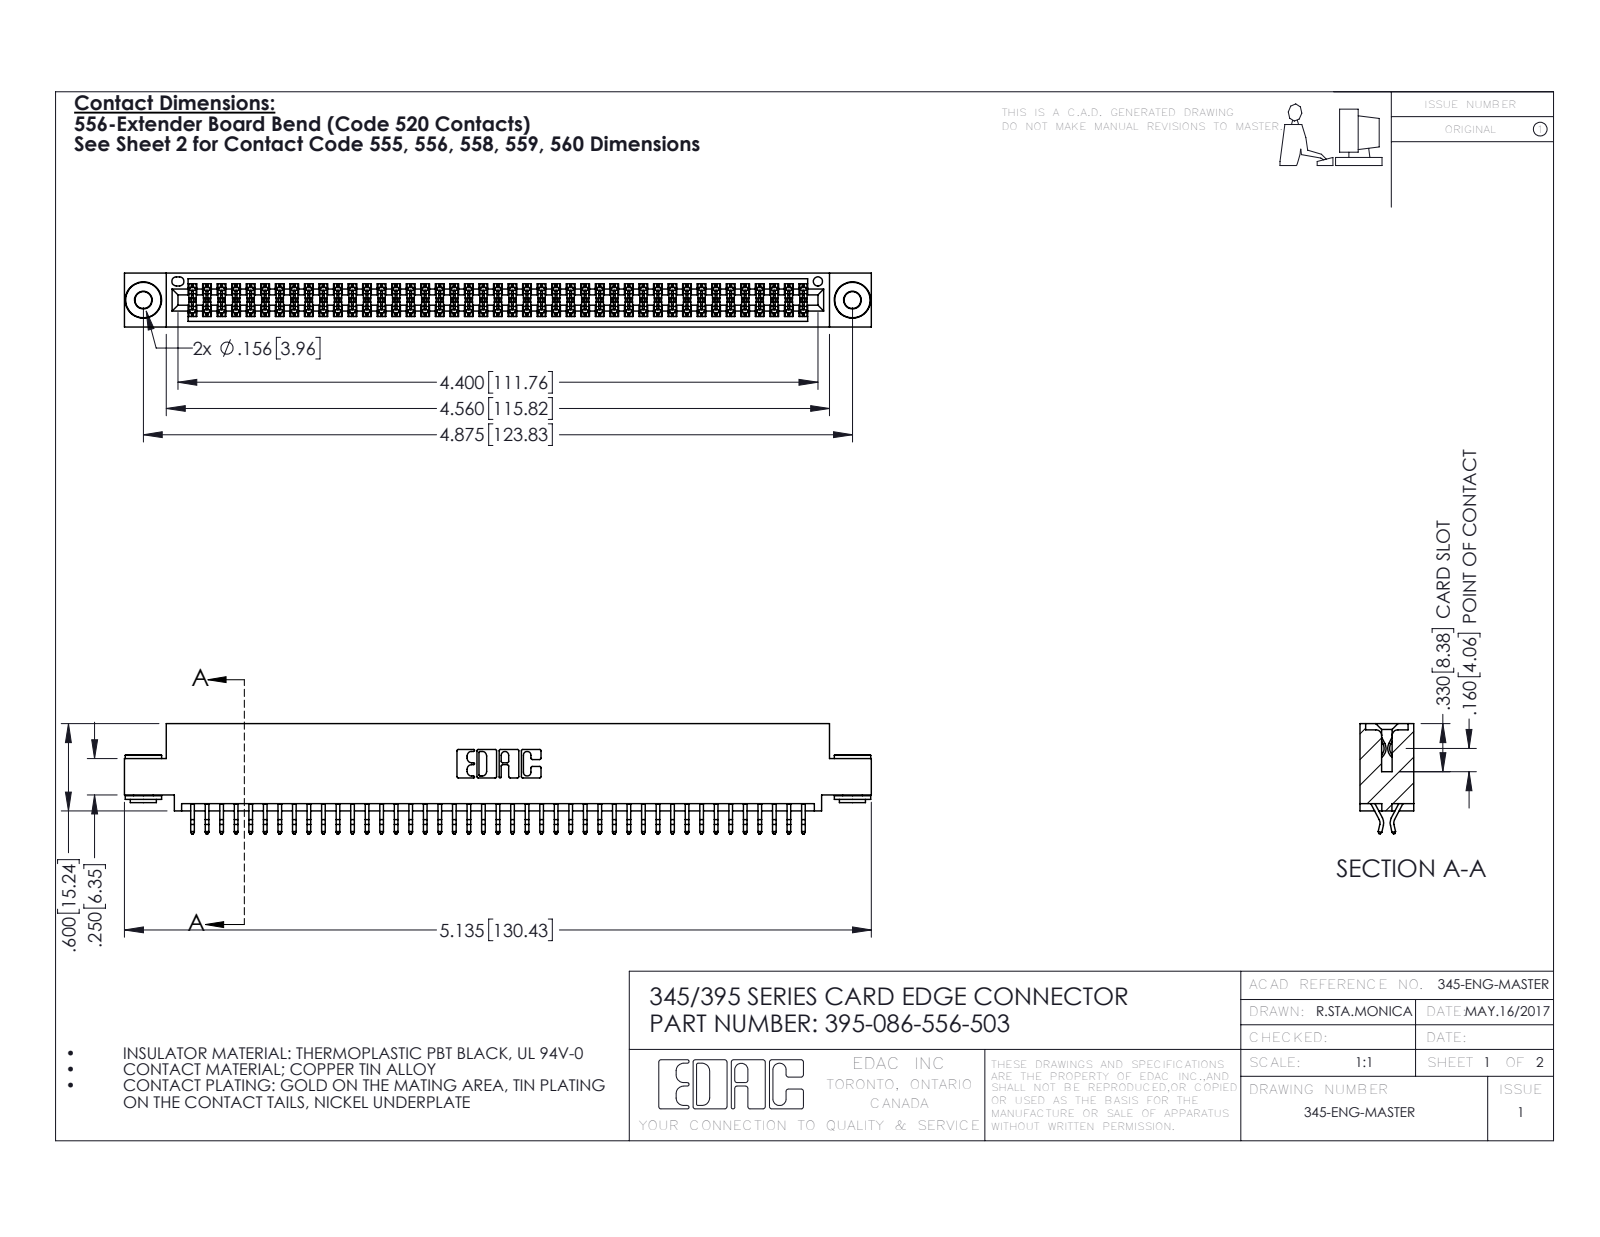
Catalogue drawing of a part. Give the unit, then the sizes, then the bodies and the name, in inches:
Units: inches
Overall size (bounding box): 5.135 × 0.757 × 0.37
Round holes (diameter × count): ⌀0.116 ×2, ⌀0.156 ×2, ⌀0.064 ×1
Round bosses / shafts (diameter × count): ⌀0.25 ×2, ⌀0.18 ×2, ⌀0.136 ×2
Partial cylindrical surfaces — rounded edges, fillets, slot ends (radius × count): R0.006 ×129, R0.01 ×22, R0.007 ×6, R0.031 ×6, R0.026 ×3, R0.01 ×2, R0.014 ×2, R0.019 ×2
Main face-to-face distances: 0.072, 0.298, 0.37, 0.025, 0.2, 0.098, 0.272, 0.225, 0.175, 0.149
Hole centre spacings: 0.27, 4.639, 4.875
Volume: 0.77 in³ · Surface area: 29.29 in²
Bodies: 89 solids, 4984 faces (3276 planar, 1700 cylindrical, 8 other)
Part name (STEP PRODUCT): 345-250-002_345-250-002-102; 345 Part_0.110 Offset - 0.156 Dia-TH; 395-086-556-503; 345-292-001_556 Tail
STEP written by: SolidWorks 2016 (CONFIG_CONTROL_DESIGN)
